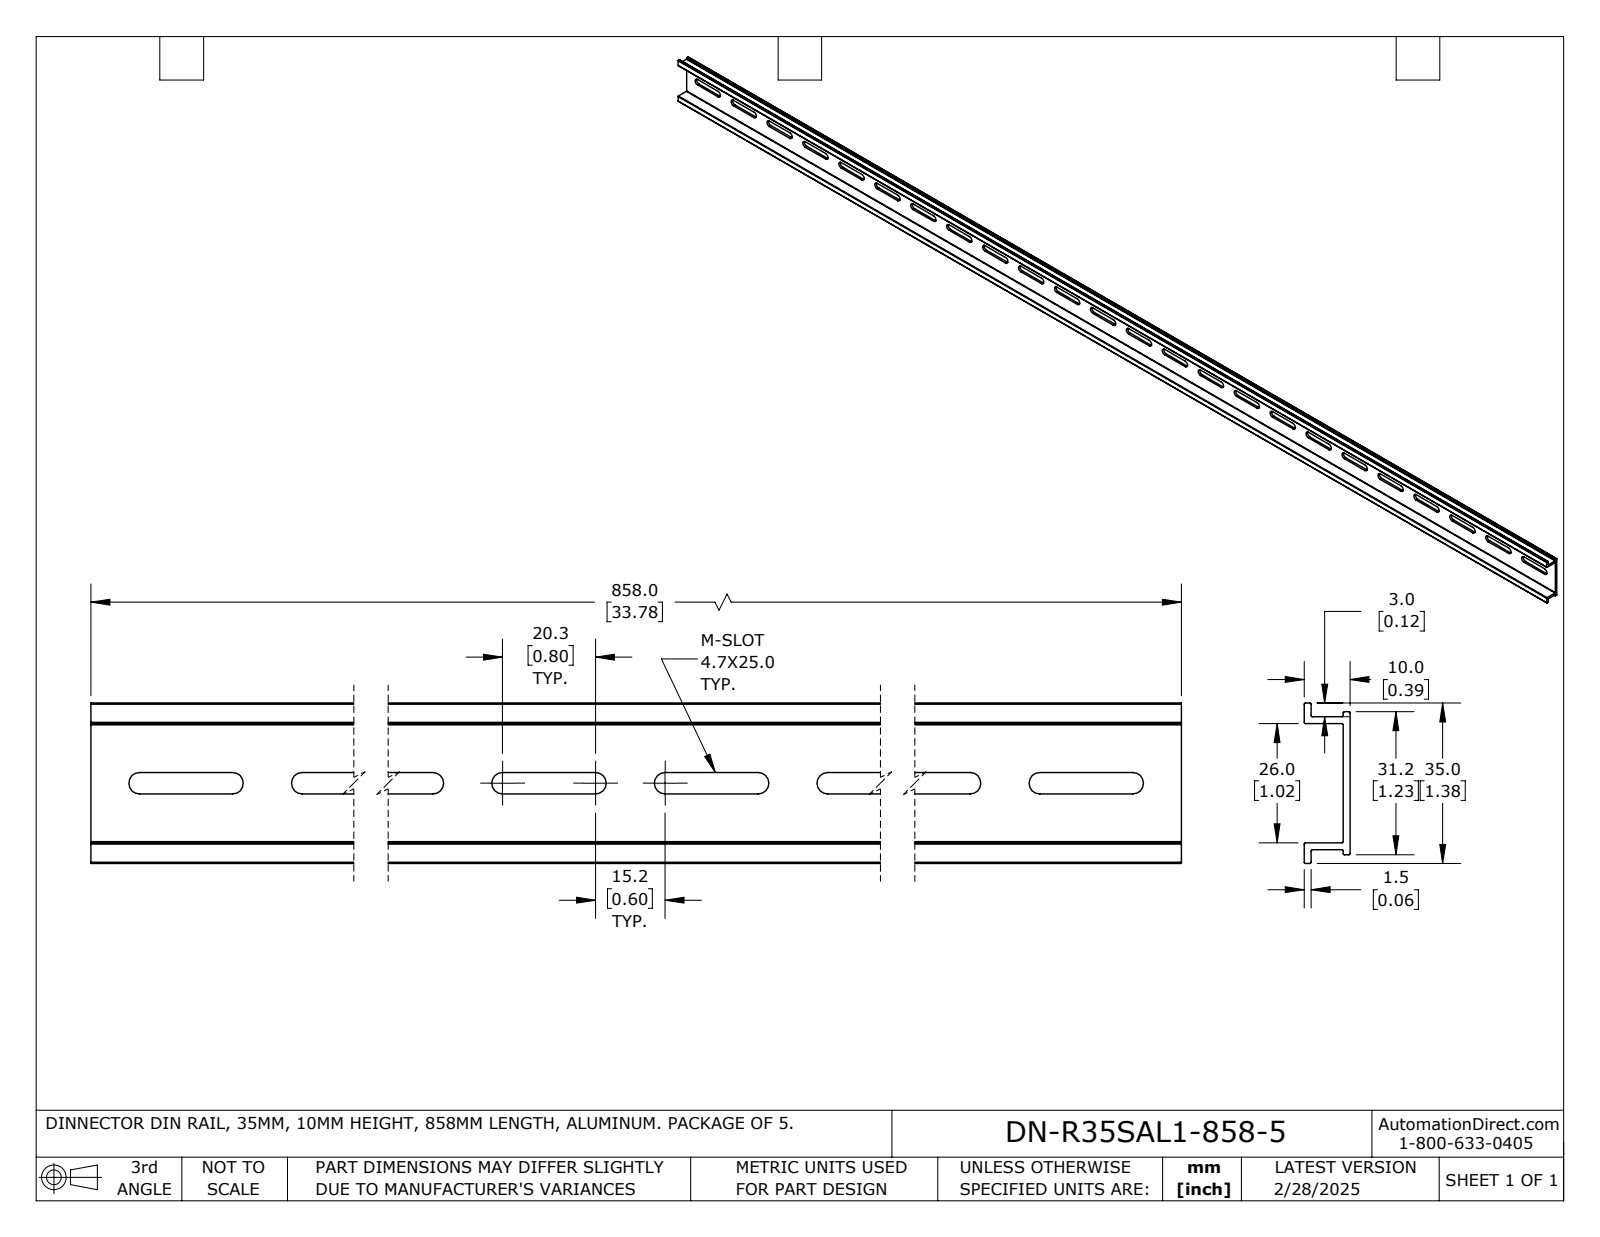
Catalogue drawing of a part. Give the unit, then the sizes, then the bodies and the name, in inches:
Units: inches
Overall size (bounding box): 33.78 × 1.378 × 0.394
Partial cylindrical surfaces — rounded edges, fillets, slot ends (radius × count): R0.093 ×48, R0.011 ×16
Main face-to-face distances: 0.059, 1.083, 0.335, 1.024, 0.394, 1.142, 0.276, 0.043, 0.102, 1.126
Volume: 4.006 in³ · Surface area: 140.7 in²
Bodies: 1 solid, 130 faces (66 planar, 64 cylindrical, 0 other)
Part name (STEP PRODUCT): DN-R35SAL1-858-5_Default
STEP written by: SolidWorks 2024 (CONFIG_CONTROL_DESIGN)
